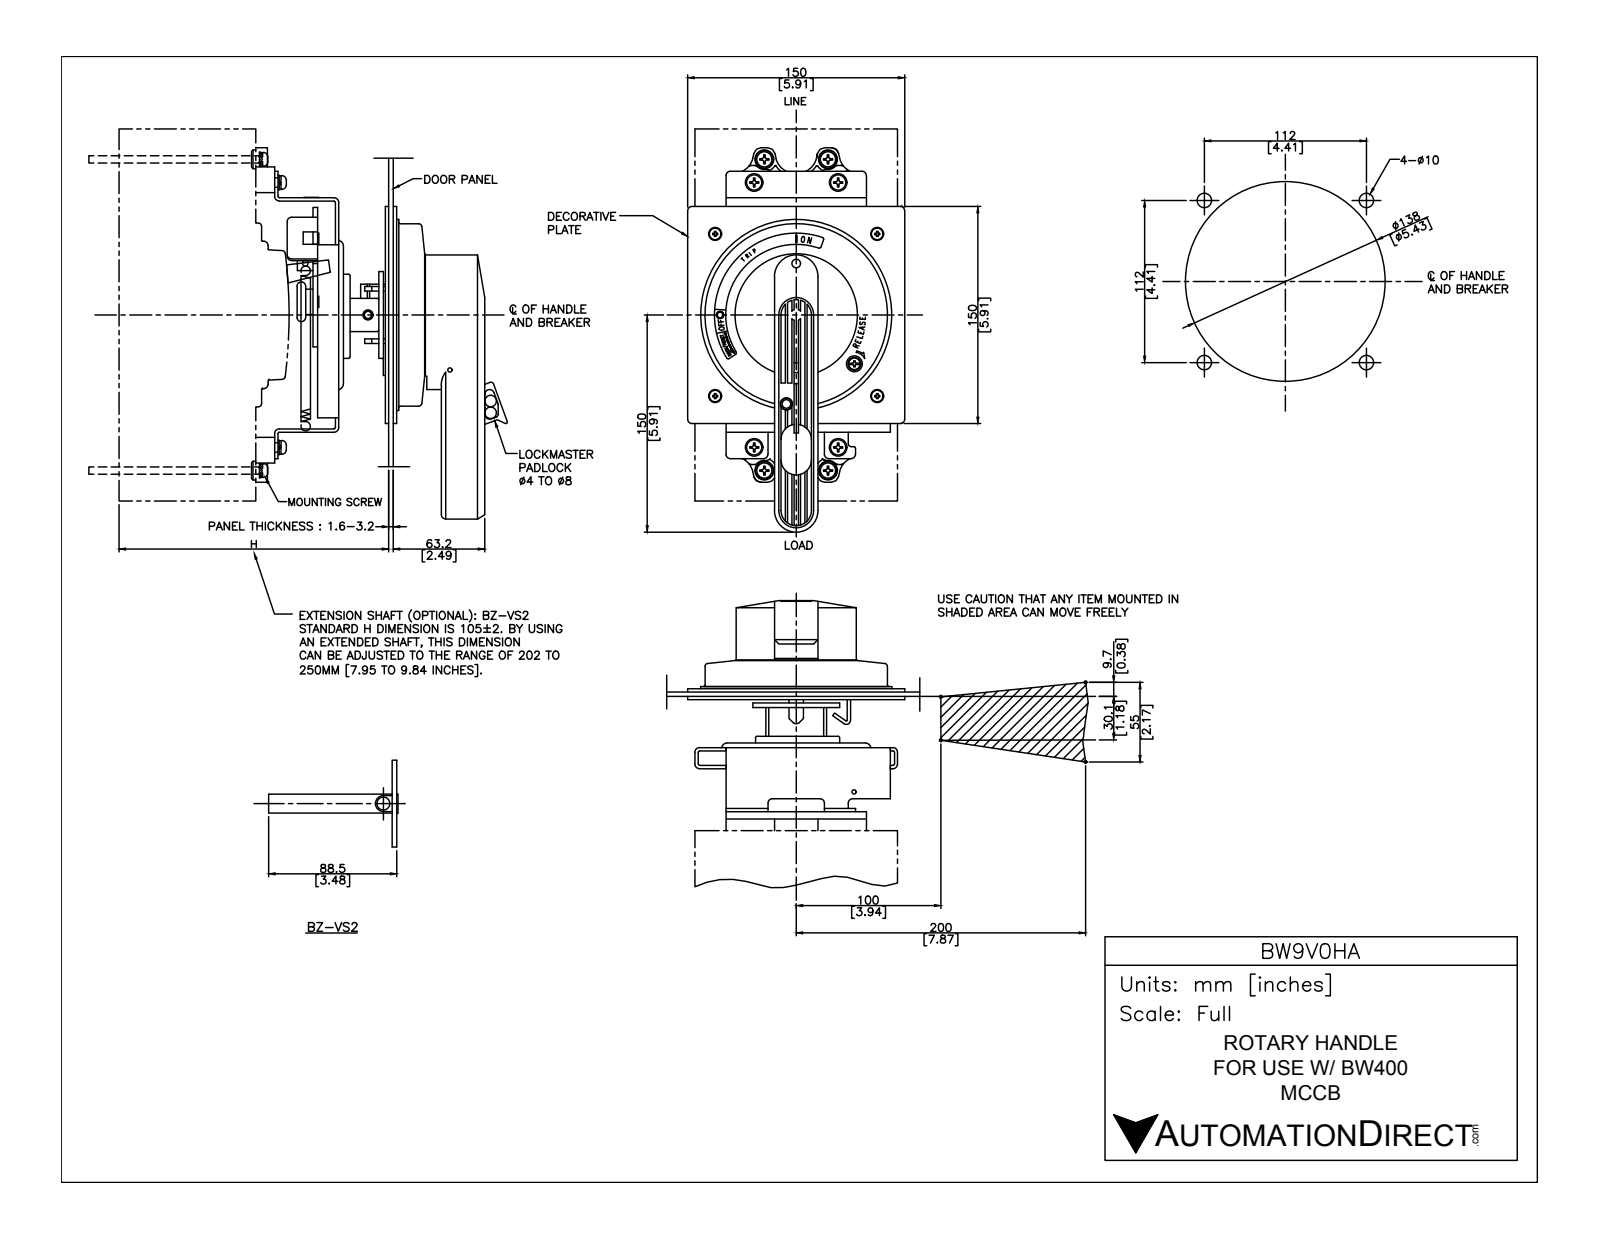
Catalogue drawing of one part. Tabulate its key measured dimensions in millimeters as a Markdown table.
| quantity | value |
| --- | --- |
| part name | BW9V0HA |
| STEP written by | SolidWorks 2018 (AUTOMOTIVE_DESIGN) |
| units | millimeters |
| bodies | 17 solids, 469 faces (215 planar, 238 cylindrical, 16 other) |
| overall size | 265.5 × 264 × 150 |
| volume | 721 900 mm³ |
| surface area | 245 700 mm² |
| round holes (diameter × count) | 6.5 × 8, 4 × 4, 8 × 4, 13 × 4, 5 × 1, 38 × 1, 84.5 × 1 |
| round bosses / shafts (diameter × count) | 10.5 × 4, 7 × 4, 6 × 4, 130 × 1, 126 × 1, 105 × 1, 84 × 1, 76 × 1 |
| partial cylindrical surfaces (radius × count) | 2 × 27, 3 × 19, 5 × 8, 7.5 × 7, 1.5 × 6, 1 × 4, 3.3 × 4, 13 × 4 |
| main face-to-face distances | 2.3, 30, 37.6, 35.3, 24.5, 7.6, 5.3, 29.8, 49.9, 27.7 |
| hole center spacings | 17.4, 44.6, 53.4, 61.7, 79.2, 92.1, 93.5, 96 |
